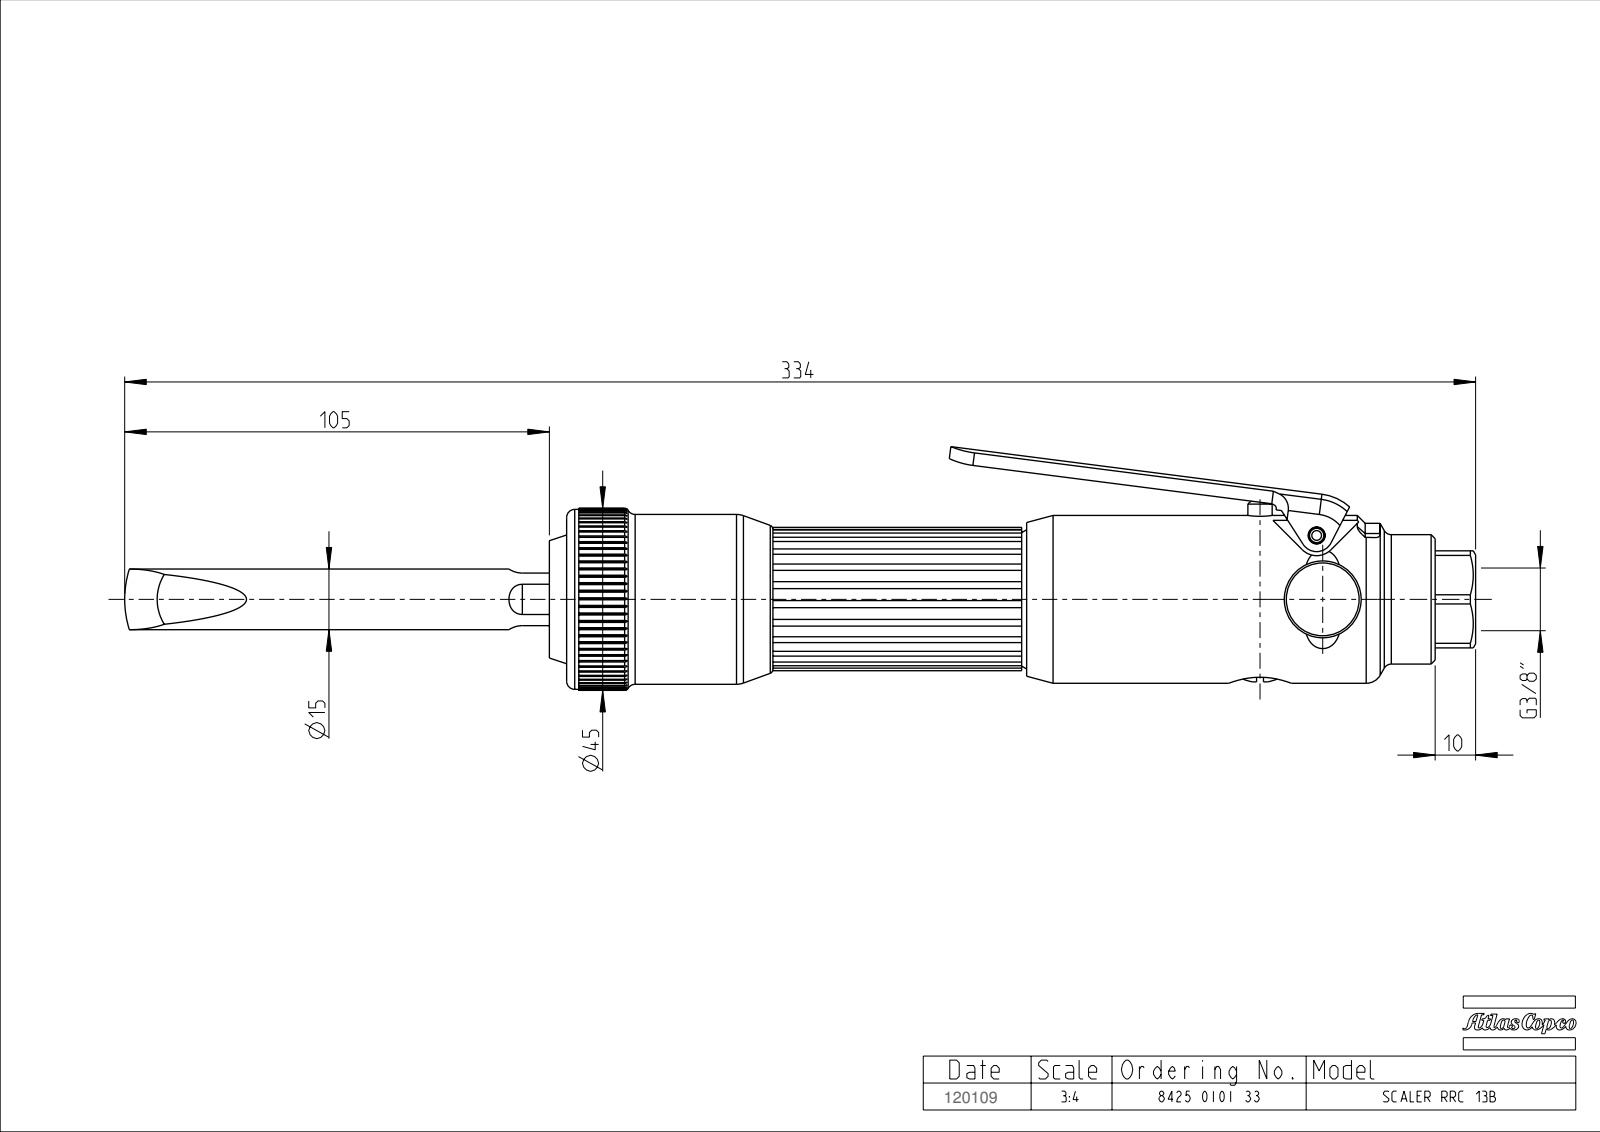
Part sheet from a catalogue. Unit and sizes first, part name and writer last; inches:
Units: inches
Overall size (bounding box): 13.15 × 2.372 × 1.915
Round holes (diameter × count): ⌀0.61 ×1, ⌀0.669 ×1
Round bosses / shafts (diameter × count): ⌀1.752 ×1, ⌀1.654 ×1, ⌀1.634 ×1, ⌀1.26 ×1, ⌀0.709 ×1, ⌀0.591 ×1, ⌀0.236 ×1
Partial cylindrical surfaces — rounded edges, fillets, slot ends (radius × count): R0.039 ×23, R0.236 ×5, R0.197 ×2, R0.295 ×2, R0.522 ×1, R0.681 ×1, R0.74 ×1, R0.886 ×1
Main face-to-face distances: 0.512, 0.02, 0.492, 0.168, 8.454, 8.622, 0.945, 0.433, 8.021, 8.189
Bodies: 0 solids, 277 faces (71 planar, 159 cylindrical, 47 other)
Part name (STEP PRODUCT): TMP13658_SW
STEP written by: PRO/ENGINEER BY PARAMETRIC TECHNOLOGY CORPORATION, 2008310 (CONFIG_CONTROL_DESIGN)
